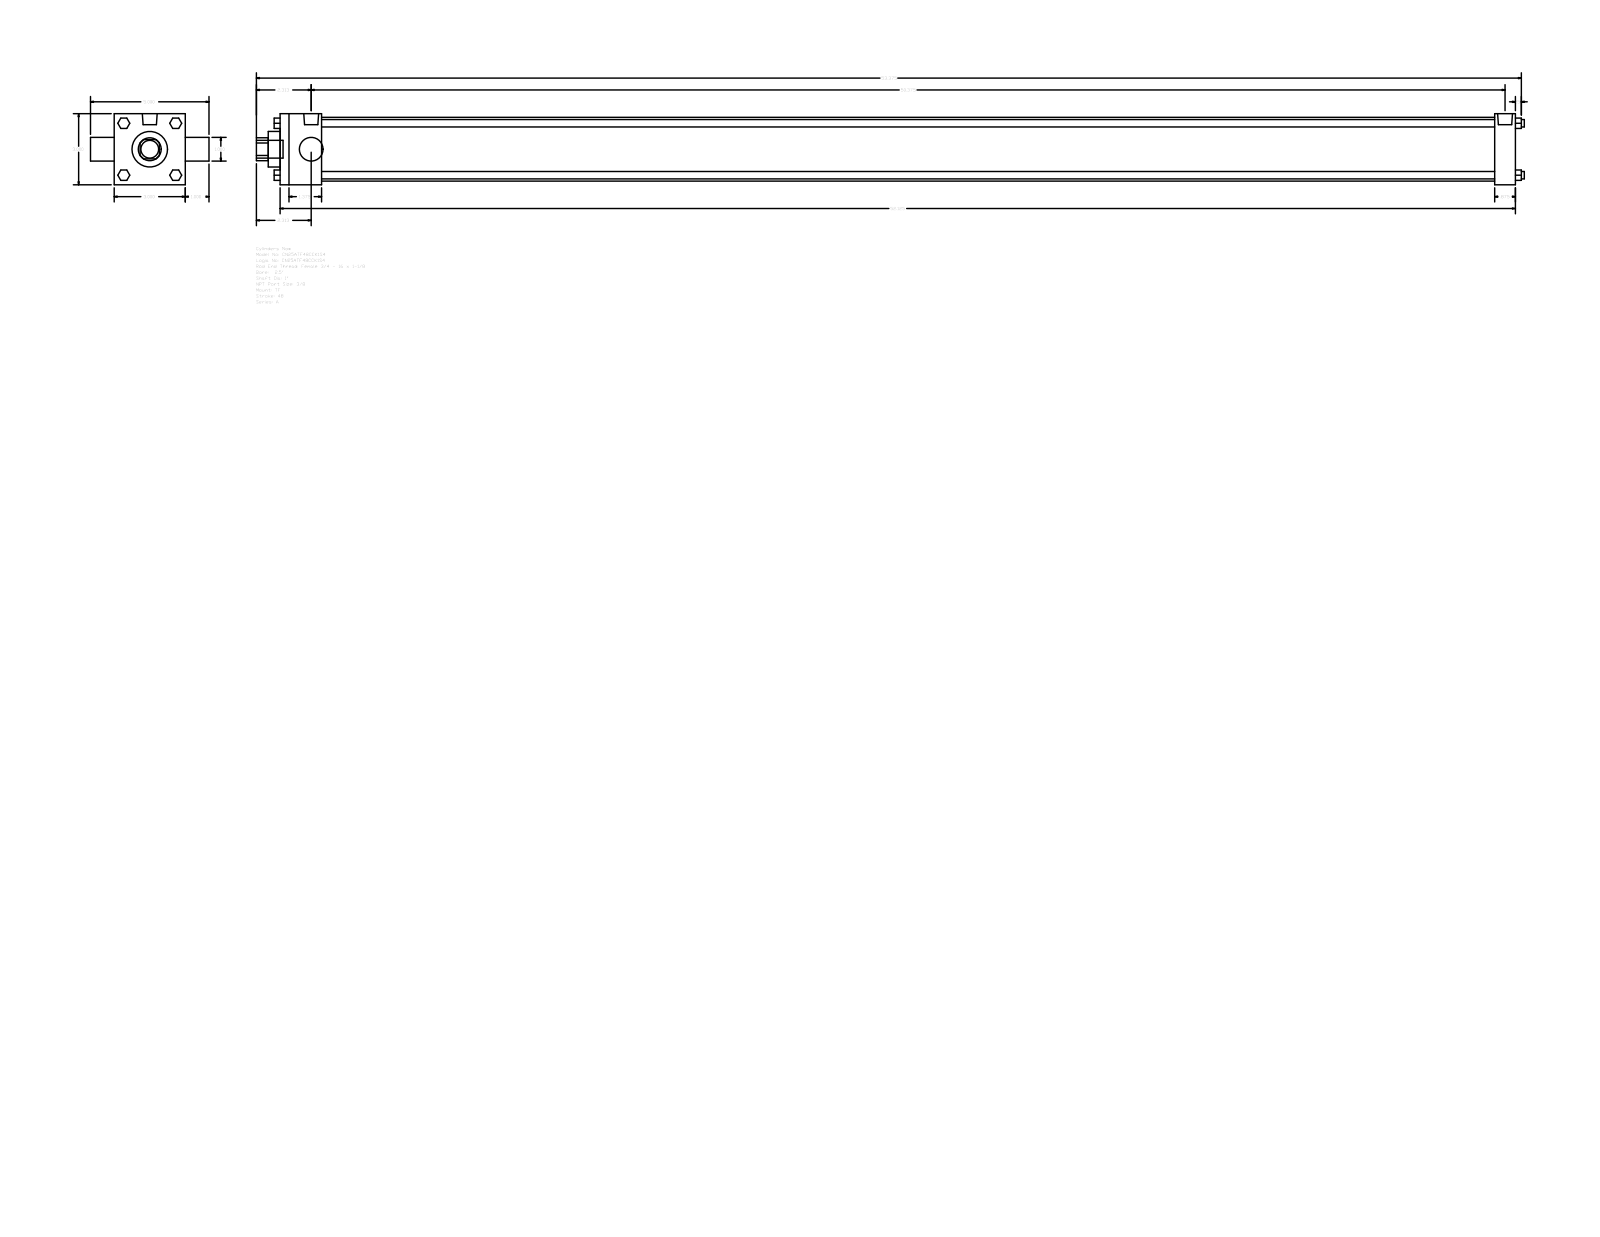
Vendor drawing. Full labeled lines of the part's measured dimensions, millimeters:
Part name (STEP PRODUCT): A_TF__0250_1
STEP written by: GSSL Pune (CONFIG_CONTROL_DESIGN)
Units: millimetres
Bodies: 0 solids, 120 faces (92 planar, 28 cylindrical, 0 other)
Overall size (bounding box): 1358.9 × 127 × 76.2
Round holes (diameter × count): ⌀25.4 ×2, ⌀38.1 ×1, ⌀68.33 ×1
Round bosses / shafts (diameter × count): ⌀7.94 ×4, ⌀5.56 ×3, ⌀15.93 ×2, ⌀19.05 ×1
Partial cylindrical surfaces — rounded edges, fillets, slot ends (radius × count): R12.29 ×1
Main face-to-face distances: 76.2, 1323.98, 44.45, 1301.75, 1257.3, 1279.53, 22.23, 25.4, 101.6, 12.7
